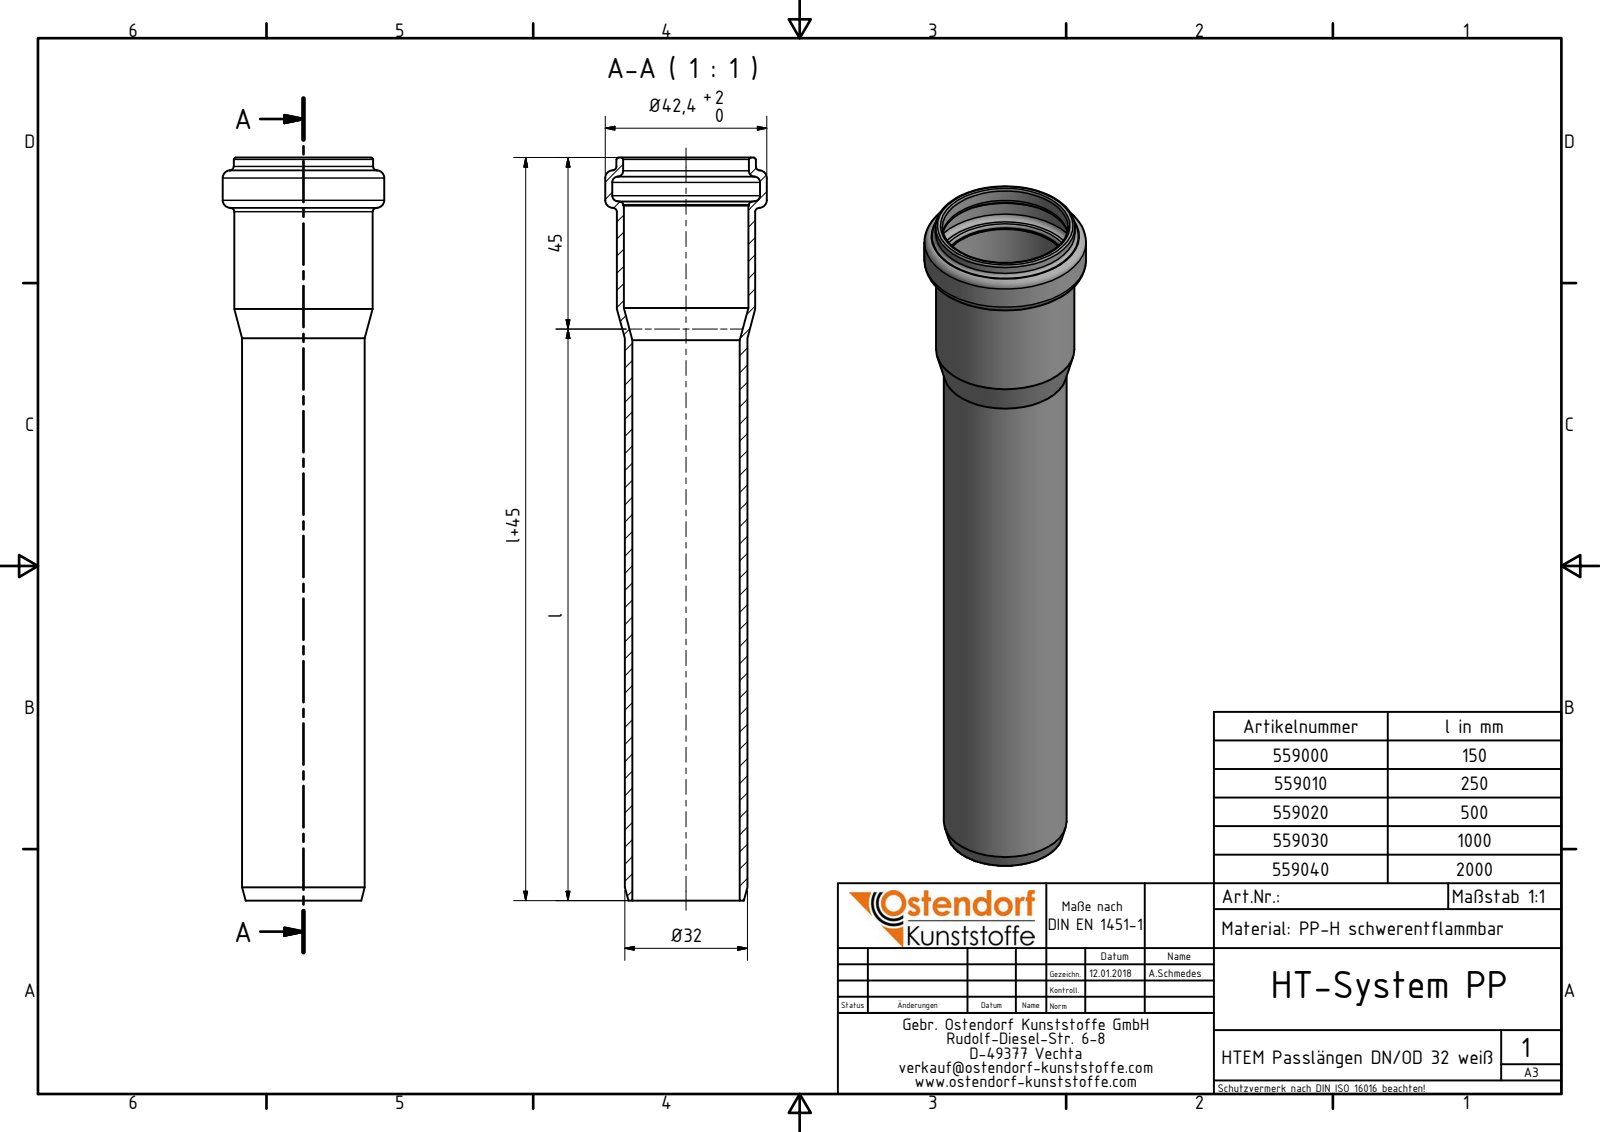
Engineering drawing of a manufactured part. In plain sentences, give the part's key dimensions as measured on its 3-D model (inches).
The part is named "559000 HTEM DN_OD 32x150 weiß". Its 3-D file was written by "Autodesk Inventor 2016 (AUTOMOTIVE_DESIGN)". It is 1 solid with 29 faces: 3 planar, 9 cylindrical and 17 other. Overall it measures 7.677 by 1.669 by 1.669 inches. Its volume is 2.34 cubic inches and its surface area 61.4 square inches. Round holes: 1 of diameter 1.11, 1 of diameter 1.287, 1 of diameter 1.299, 1 of diameter 1.528. Round bosses or shafts: 1 of diameter 1.669, 1 of diameter 1.441, 1 of diameter 1.429, 1 of diameter 1.268. The main face-to-face distances are 7.677, 7.18, 0.497.
